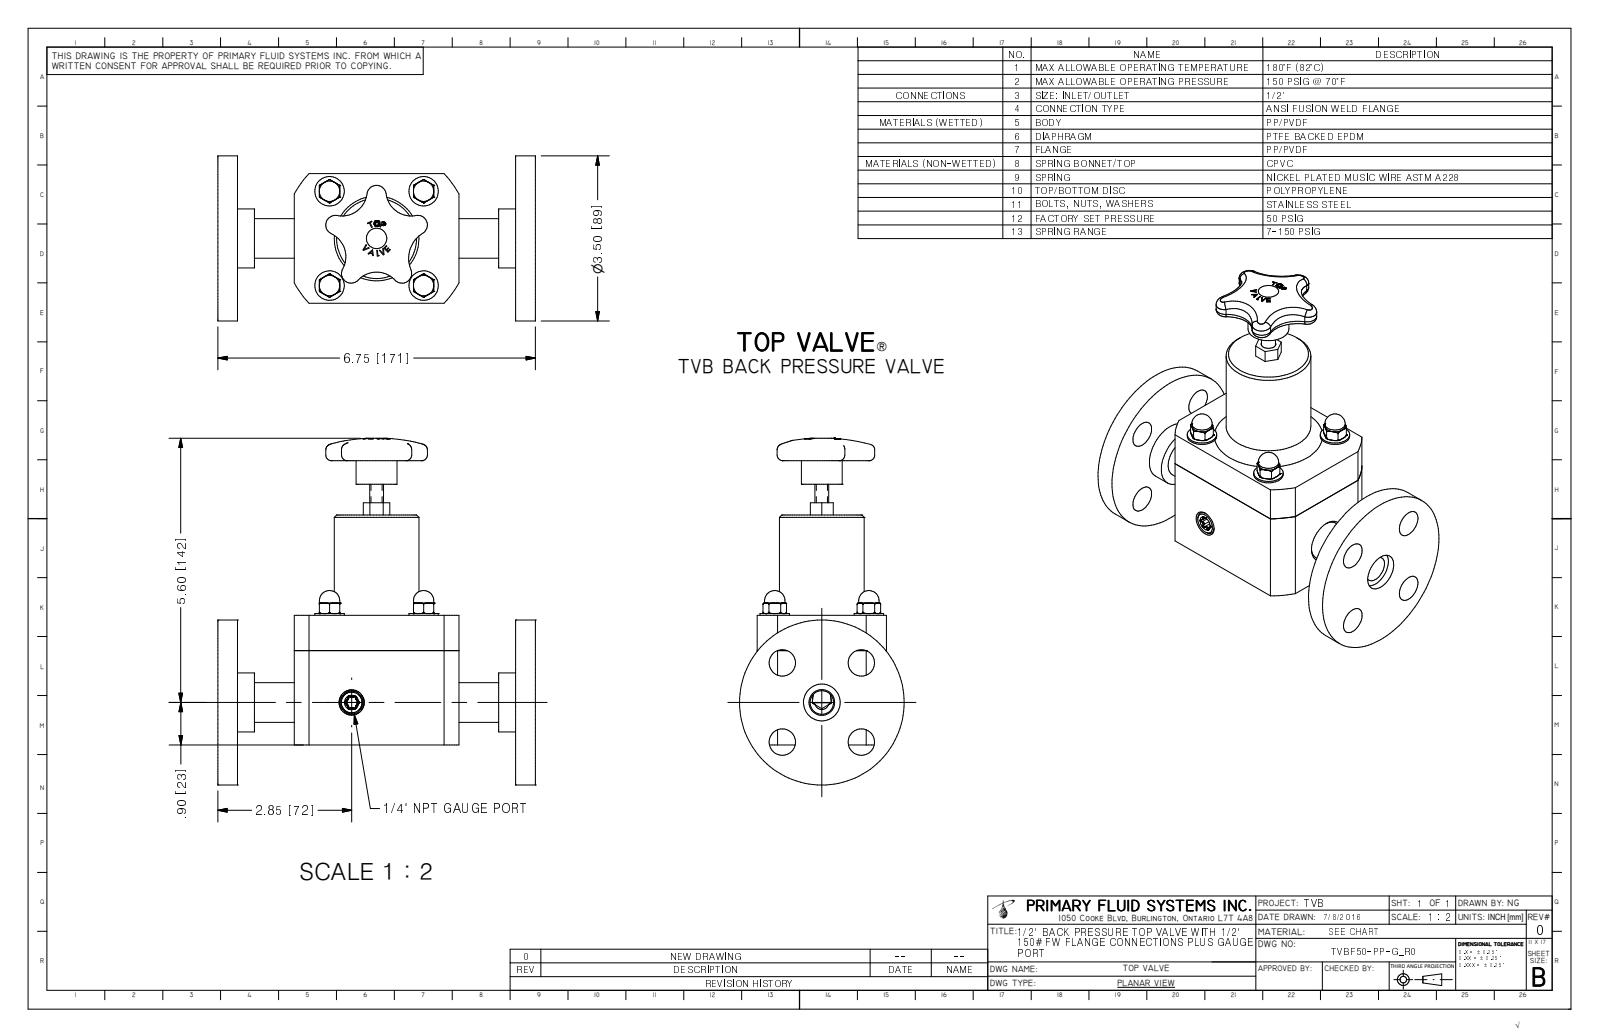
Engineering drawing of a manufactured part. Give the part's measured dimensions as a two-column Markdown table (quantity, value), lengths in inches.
| quantity | value |
| --- | --- |
| part name | TVBF50-PP-G_R0 |
| STEP written by | Autodesk Inventor 2009 (AUTOMOTIVE_DESIGN) |
| units | inches |
| bodies | 1 solid, 394 faces (163 planar, 70 cylindrical, 161 other) |
| overall size | 7.352 × 6.75 × 3.5 |
| volume | 40.82 in³ |
| surface area | 144.4 in² |
| round holes (diameter × count) | 0.175 × 4, 0.56 × 4, 0.281 × 1, 0.546 × 1, 0.78 × 1 |
| round bosses / shafts (diameter × count) | 0.625 × 4, 0.433 × 4, 0.375 × 4, 3.5 × 1, 1.8 × 1, 1.25 × 1, 0.87 × 1, 0.84 × 1 |
| partial cylindrical surfaces (radius × count) | 0.027 × 6, 0.085 × 5, 0.205 × 5, 0.536 × 4, 0.656 × 4, 0.625 × 1, 0.745 × 1, 1.988 × 1 |
| main face-to-face distances | 0.42, 6.33, 1.625, 5.125, 1.205, 4.705, 6.75, 2.75, 5.91, 3.5 |
| hole center spacings | 1.188, 1.68, 2, 2.375, 2.828 |
